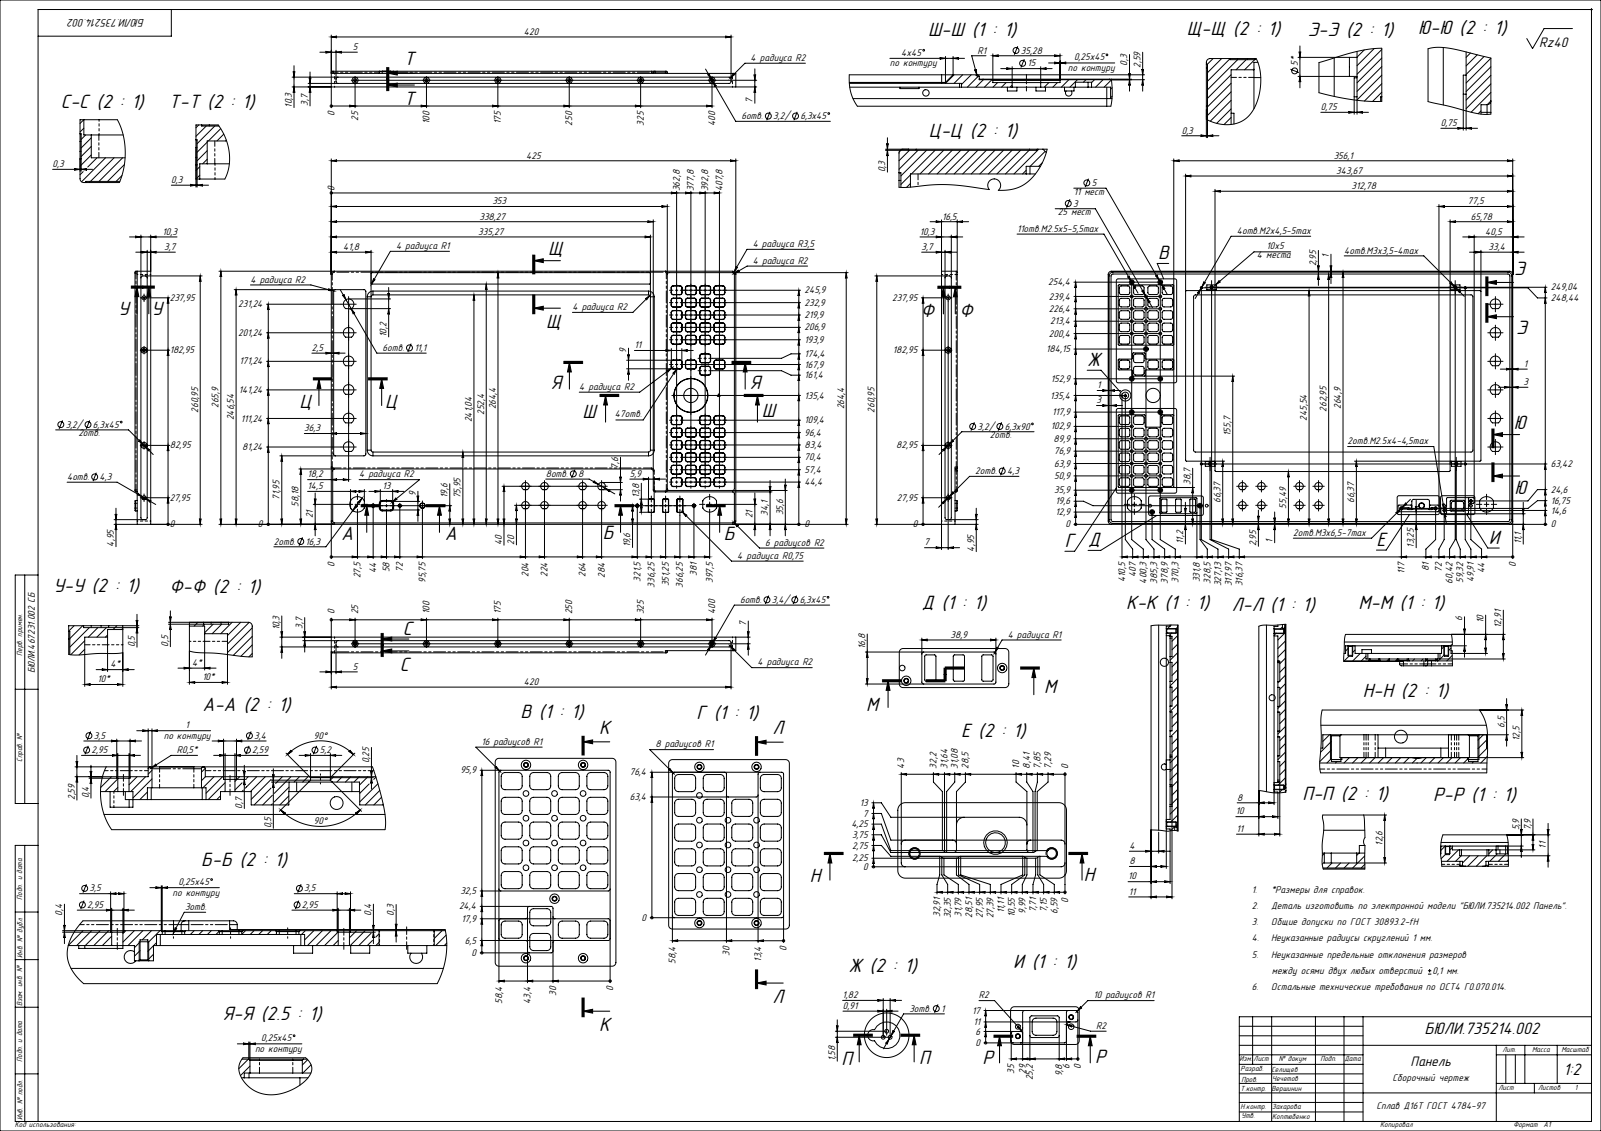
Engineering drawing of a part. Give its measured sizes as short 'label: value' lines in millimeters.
name: БЮЛИ.735214.002 Панель
written by: SolidWorks 2018 (CONFIG_CONTROL_DESIGN)
unit: mm
bodies: 1 solid, 1583 faces (656 planar, 610 cylindrical, 317 other)
size: 425 × 265.9 × 16.5
volume: 281 706 mm³; area: 169 114 mm²
holes: 13× ⌀2.05, 8× ⌀3.2, 8× ⌀8, 7× ⌀3.4, 6× ⌀2.5, 6× ⌀11.1, 4× ⌀1.6, 3× ⌀1, 3× ⌀2.95, 3× ⌀3.5, 2× ⌀4.3, 1× ⌀2.59
bosses: 25× ⌀3, 11× ⌀5
rounds: 233× R2, 90× R1, 26× R0.75, 4× R0.5, 4× R3, 4× R3.5, 4× R4, 2× R8.15
face distances: 3.91, 1, 2, 6.5, 2.59, 4.5, 1.91, 2.29, 6.2, 4.2
hole spacings: 75, 30, 150, 225, 5, 18.74, 19.04, 28.44
